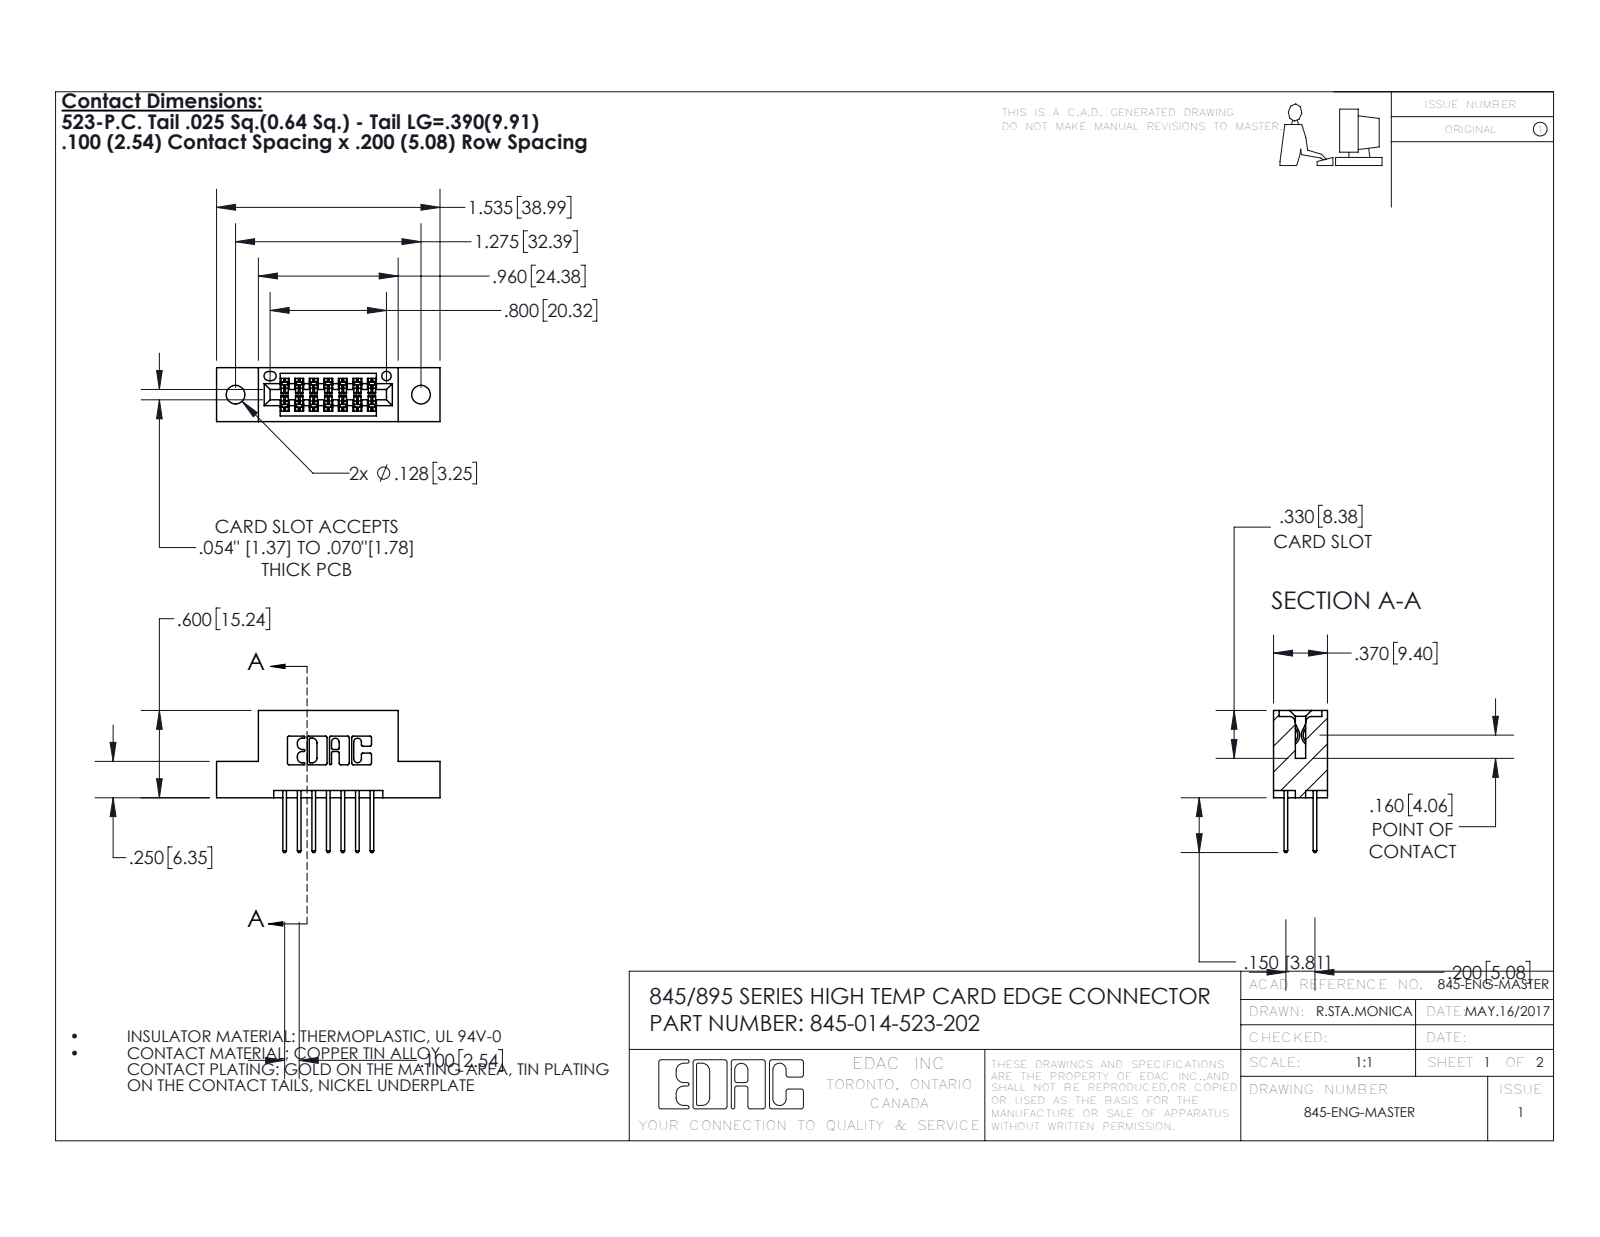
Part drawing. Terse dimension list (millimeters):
name: 345-292-001_345-293-123; 345-014-523-202; 345 Part_Flush Mounting Lugs - 0.128 Dia
written by: SolidWorks 2016 (CONFIG_CONTROL_DESIGN)
unit: mm
bodies: 15 solids, 826 faces (542 planar, 284 cylindrical, 0 other)
size: 39 × 24.8 × 9.4
volume: 3 460 mm³; area: 4 285 mm²
holes: 2× ⌀3.3, 1× ⌀1.6
rounds: 22× R0.3, 21× R0.2, 14× R0.3, 6× R0.2, 6× R0.8, 3× R0.7, 2× R0.4, 2× R0.5
face distances: 5.1, 7.6, 1.8, 9.4, 2.5, 2.5, 6.9, 0.6, 5.7, 7.6
hole spacings: 6.9, 26.5, 32.4
